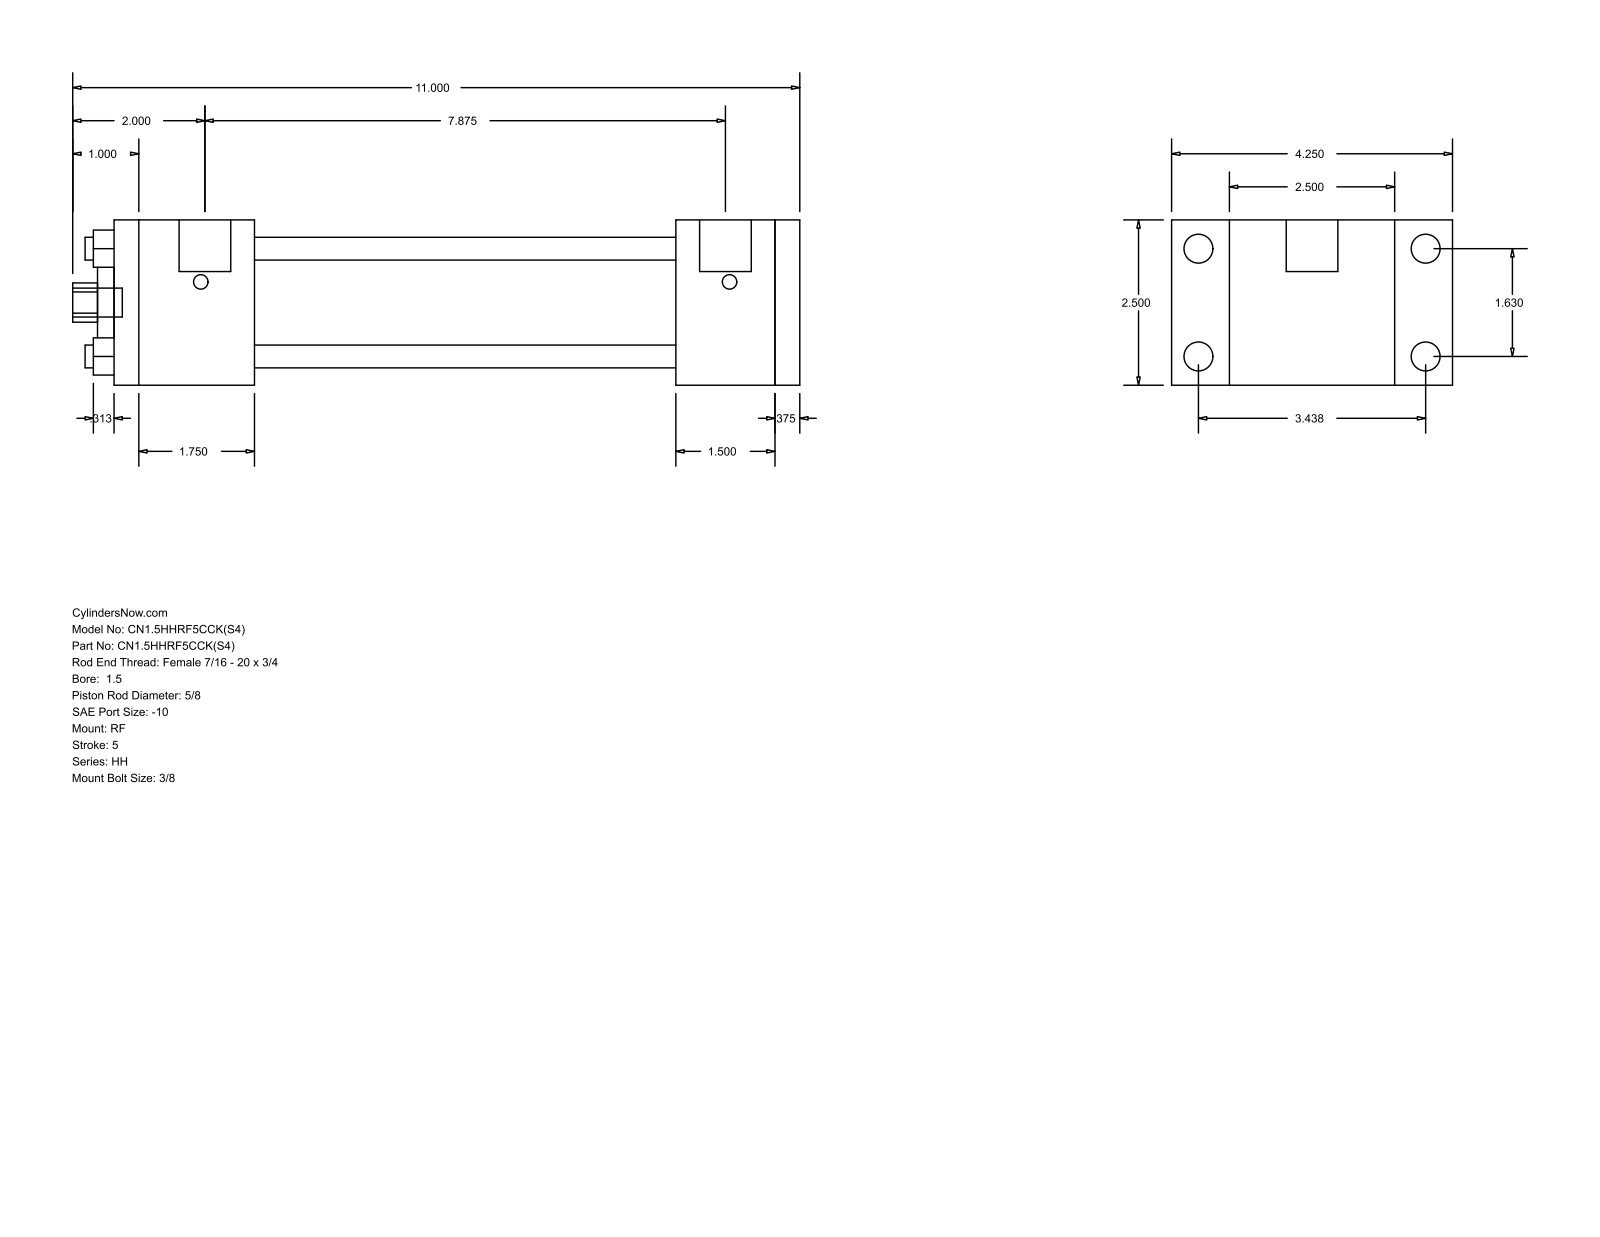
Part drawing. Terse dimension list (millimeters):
name: HH_RF__0150_0.625
written by: GSSL Pune (CONFIG_CONTROL_DESIGN)
unit: mm
bodies: 0 solids, 92 faces (64 planar, 28 cylindrical, 0 other)
size: 279.4 × 107.95 × 63.5
holes: 4× ⌀8.76, 1× ⌀15.88, 1× ⌀28.57, 1× ⌀44.45
bosses: 4× ⌀11.13, 4× ⌀5.56, 2× ⌀19.84, 1× ⌀11.11
rounds: 1× R7.54
face distances: 63.5, 263.52, 9.52, 38.1, 254, 53.97, 215.9, 161.93, 200.03, 209.55
hole spacings: 29.27, 41.4, 58.55
